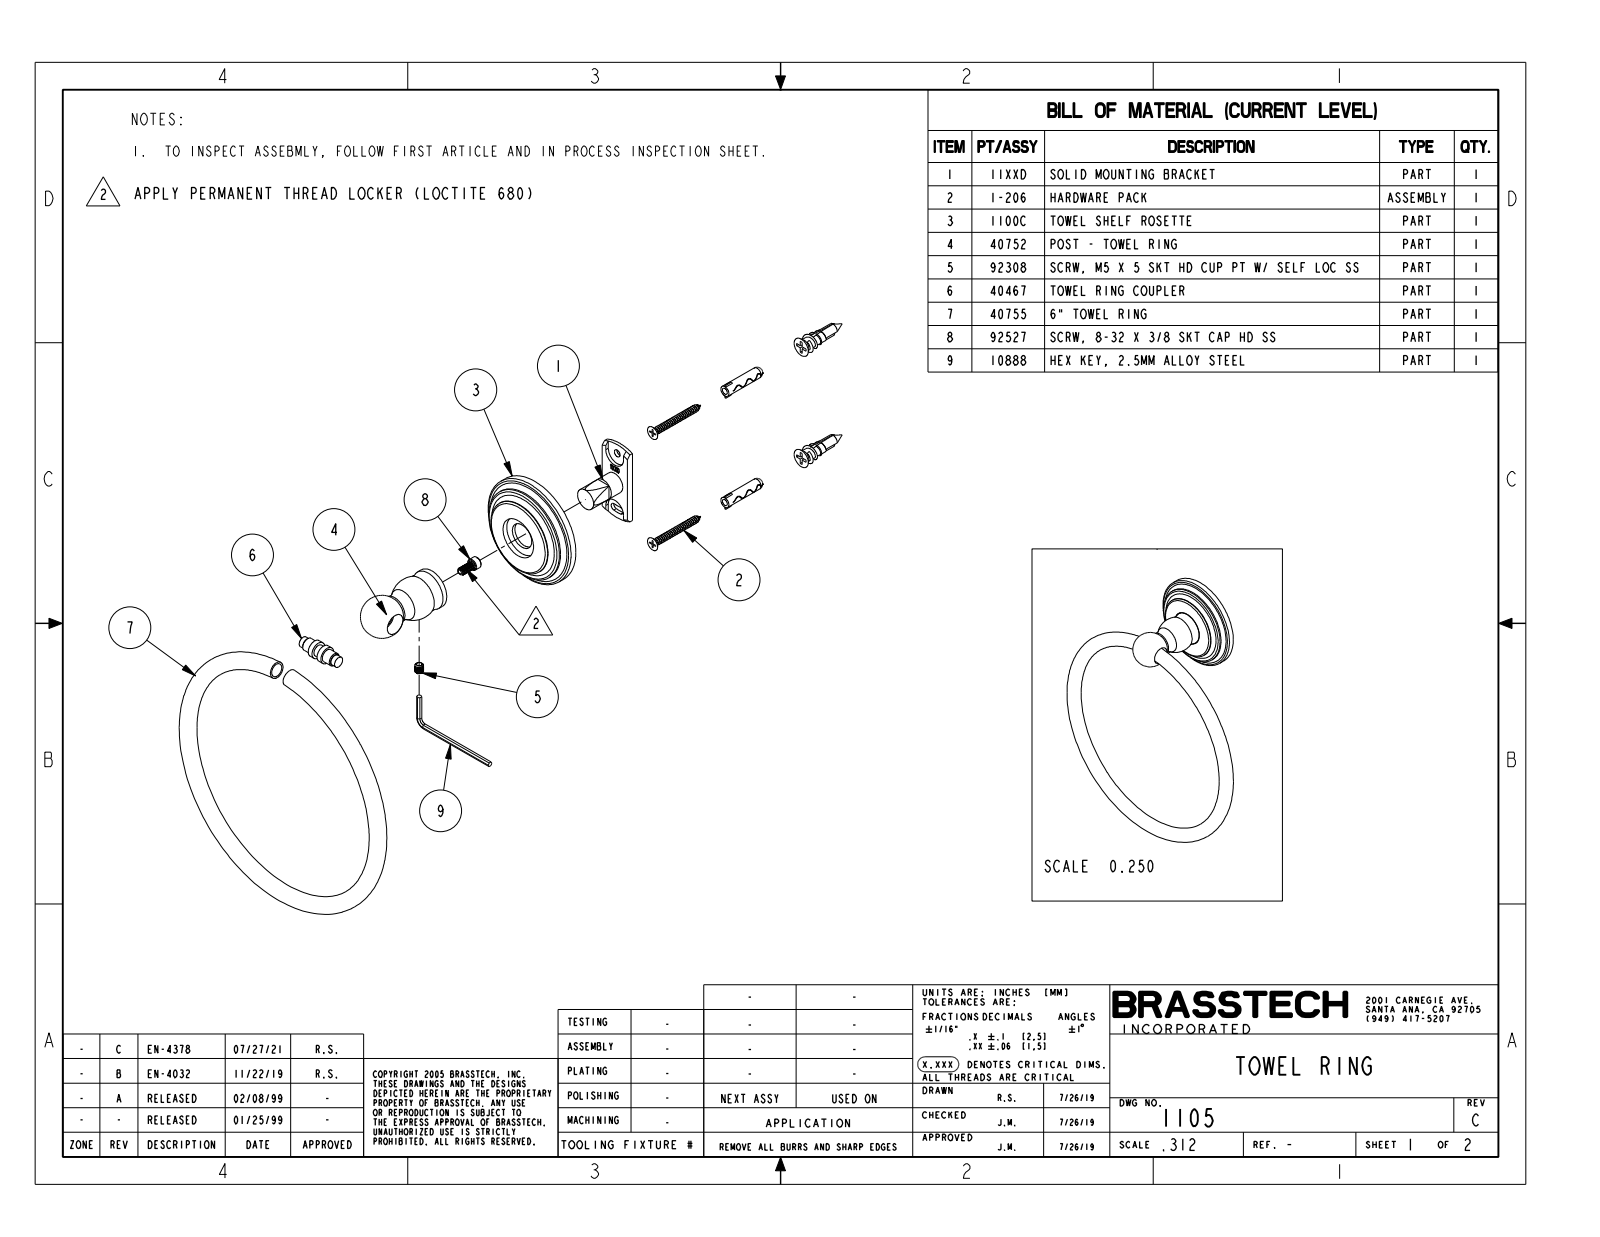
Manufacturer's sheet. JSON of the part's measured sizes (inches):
{"part_name": "1105", "step_written_by": "CREO PARAMETRIC BY PTC INC, 2018400 (AUTOMOTIVE_DESIGN)", "units": "inches", "bodies": {"solids": 1, "faces": 32, "planar": 4, "cylindrical": 6, "other": 22}, "overall_size": [7.378, 6.3, 2.422], "volume_in3": 5.132, "surface_area_in2": 39.14, "round_bosses_or_shafts": [[2.56, 1], [2.182, 1], [1.748, 1]], "face_to_face_distances": [0.512, 0.362, 0.15, 0.189, 0.173, 0.323]}
